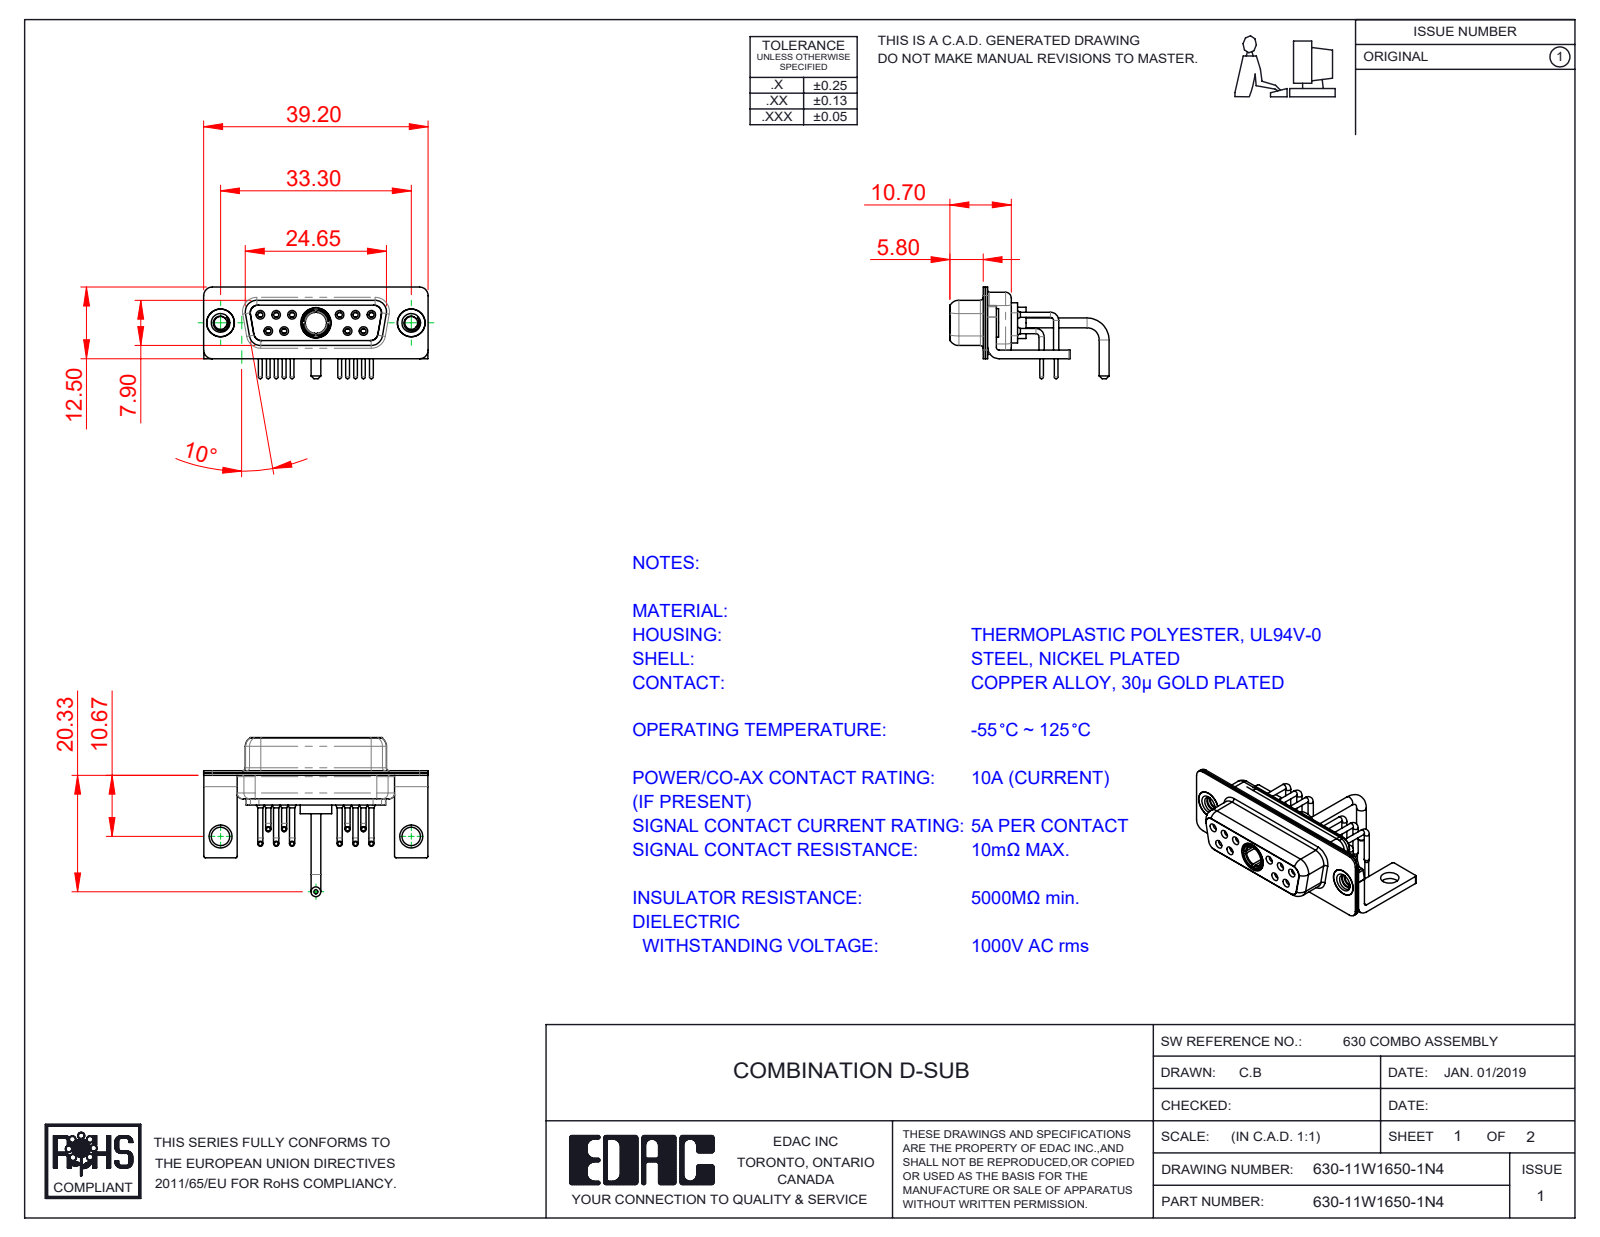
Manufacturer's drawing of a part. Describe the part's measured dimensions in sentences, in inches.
The part is named "630Combo Housing_11W1; Power Socket_Ext 10A RA; 630Combo Shell Rear_15 Contacts; 630Combo Threaded Rivet_3 (+5 more)". Its 3-D file was written by "SolidWorks 2020 (CONFIG_CONTROL_DESIGN)". It is 19 solids with 927 faces: 266 planar, 410 cylindrical and 251 other. Overall it measures 1.543 by 1.094 by 0.63 inches. Its volume is 0.175 cubic inches and its surface area 10.61 square inches. Round holes: 10 of diameter 0.035, 10 of diameter 0.043, 10 of diameter 0.059, 10 of diameter 0.079, 6 of diameter 0.067, 4 of diameter 0.063, 3 of diameter 0.191, 2 of diameter 0.089, 2 of diameter 0.126, 2 of diameter 0.157, 2 of diameter 0.159, 1 of diameter 0.146. Round bosses or shafts: 10 of diameter 0.035, 10 of diameter 0.026, 6 of diameter 0.063, 2 of diameter 0.197, 2 of diameter 0.195, 2 of diameter 0.189, 2 of diameter 0.067, 1 of diameter 0.217. Partial cylindrical surfaces (rounded edges, fillets, slot ends): 16 of radius 0.01, 16 of radius 0.059, 13 of radius 0.079, 12 of radius 0.053, 8 of radius 0.063, 5 of radius 0.02, 4 of radius 0.024, 4 of radius 0.026. The main face-to-face distances are 0.016, 0.031, 0.055, 0.018, 0.333, 0.059, 0.071, 0.35, 0.244, 0.091. The hole center spacings are 0.124, 0.109, 0.545, 0.436, 0.654, 0.198, 0.198, 0.218.
